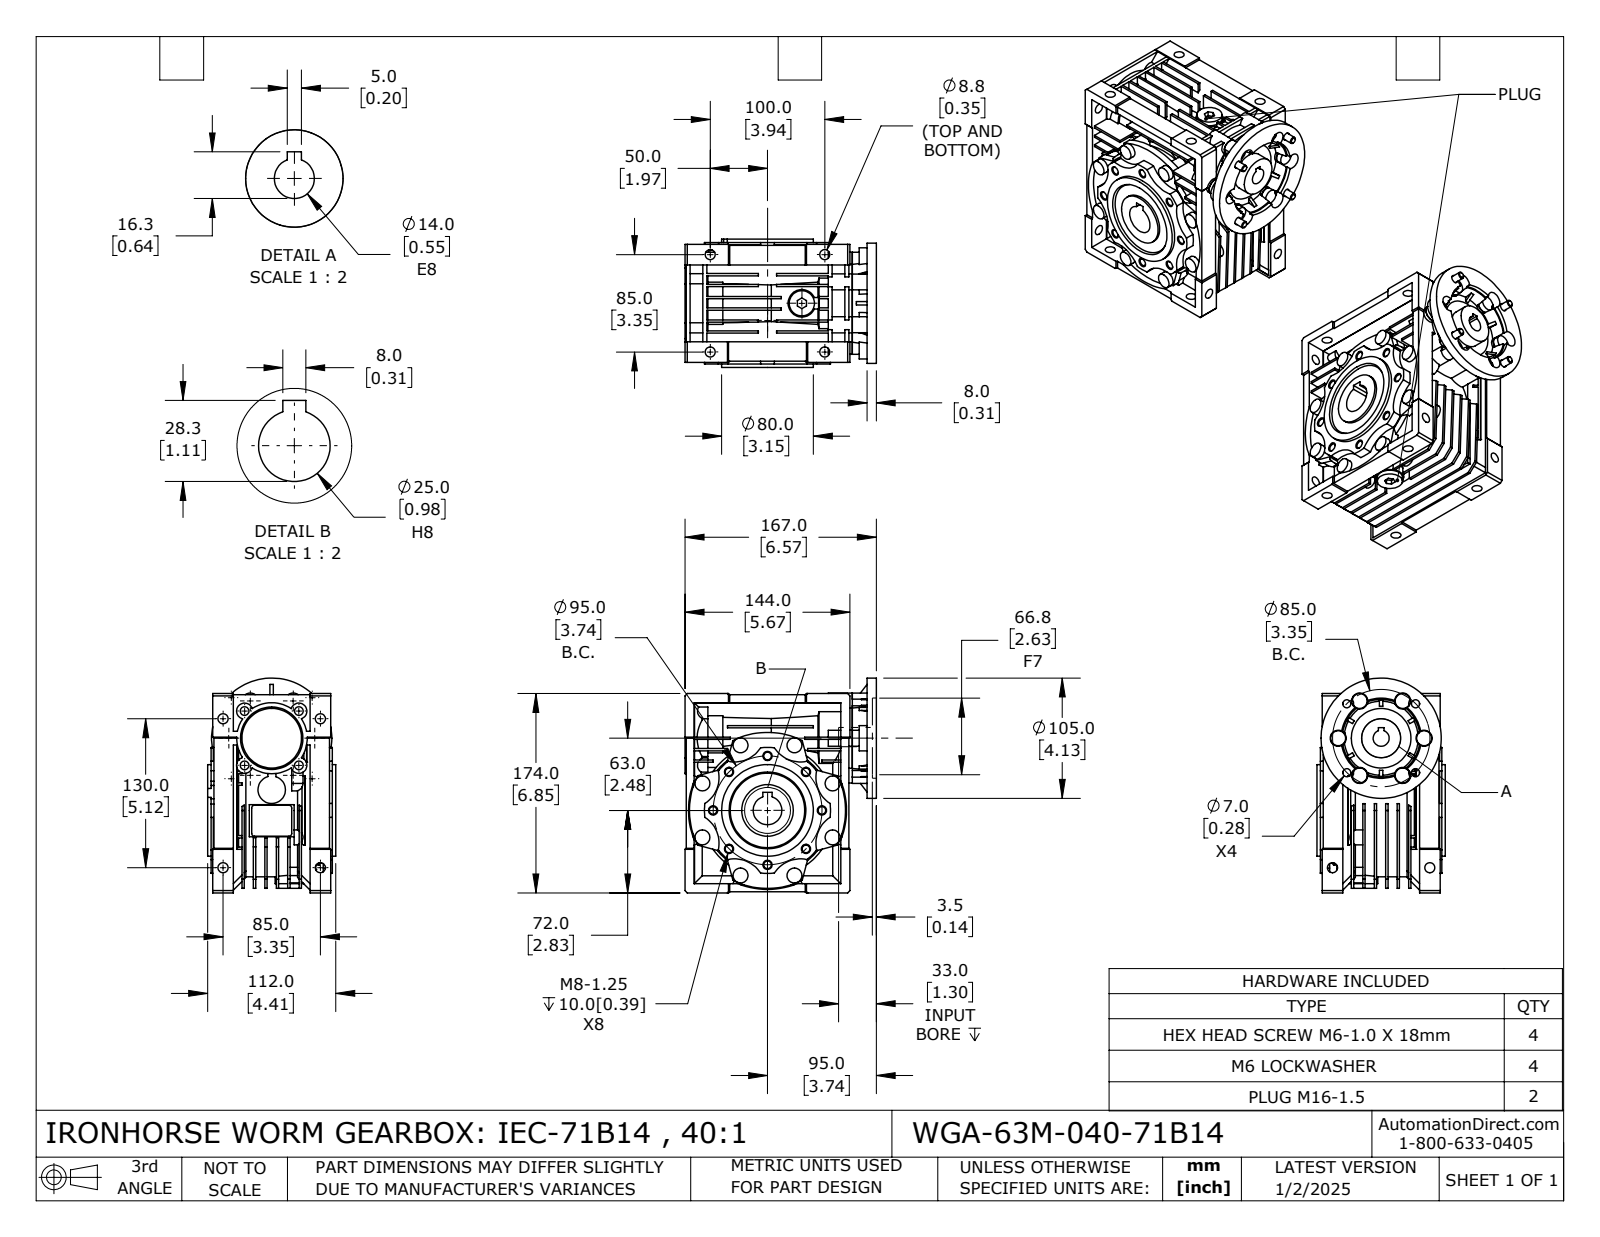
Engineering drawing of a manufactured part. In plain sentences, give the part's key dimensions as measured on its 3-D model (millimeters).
The part is named "WGA-63M-040-71B14". Its 3-D file was written by "SolidWorks 2024 (CONFIG_CONTROL_DESIGN)". It is 16 solids with 1428 faces: 836 planar, 417 cylindrical and 175 other. Overall it measures 187.5 by 175.5 by 112 millimeters. Its volume is 1 817 000 cubic millimeters and its surface area 341 752 square millimeters. Round holes: 8 of diameter 6.65, 8 of diameter 8.78, 4 of diameter 6.1, 4 of diameter 7, 4 of diameter 7.56, 2 of diameter 14.5, 1 of diameter 14, 1 of diameter 15, 1 of diameter 25, 1 of diameter 34, 1 of diameter 37, 1 of diameter 45. Round bosses or shafts: 14 of diameter 13, 4 of diameter 14, 4 of diameter 12.2, 4 of diameter 6, 3 of diameter 24, 2 of diameter 22, 2 of diameter 15.8, 2 of diameter 13.7. Partial cylindrical surfaces (rounded edges, fillets, slot ends): 12 of radius 7, 8 of radius 27, 6 of radius 6.98, 6 of radius 11, 4 of radius 2.5, 4 of radius 6, 1 of radius 8.35, 1 of radius 29.5. The main face-to-face distances are 10, 8, 20, 2, 30, 7, 12, 40, 18, 1. The hole center spacings are 36.36, 47.5, 54.12, 67.18, 87.77, 8.99, 33.5, 42.5.
